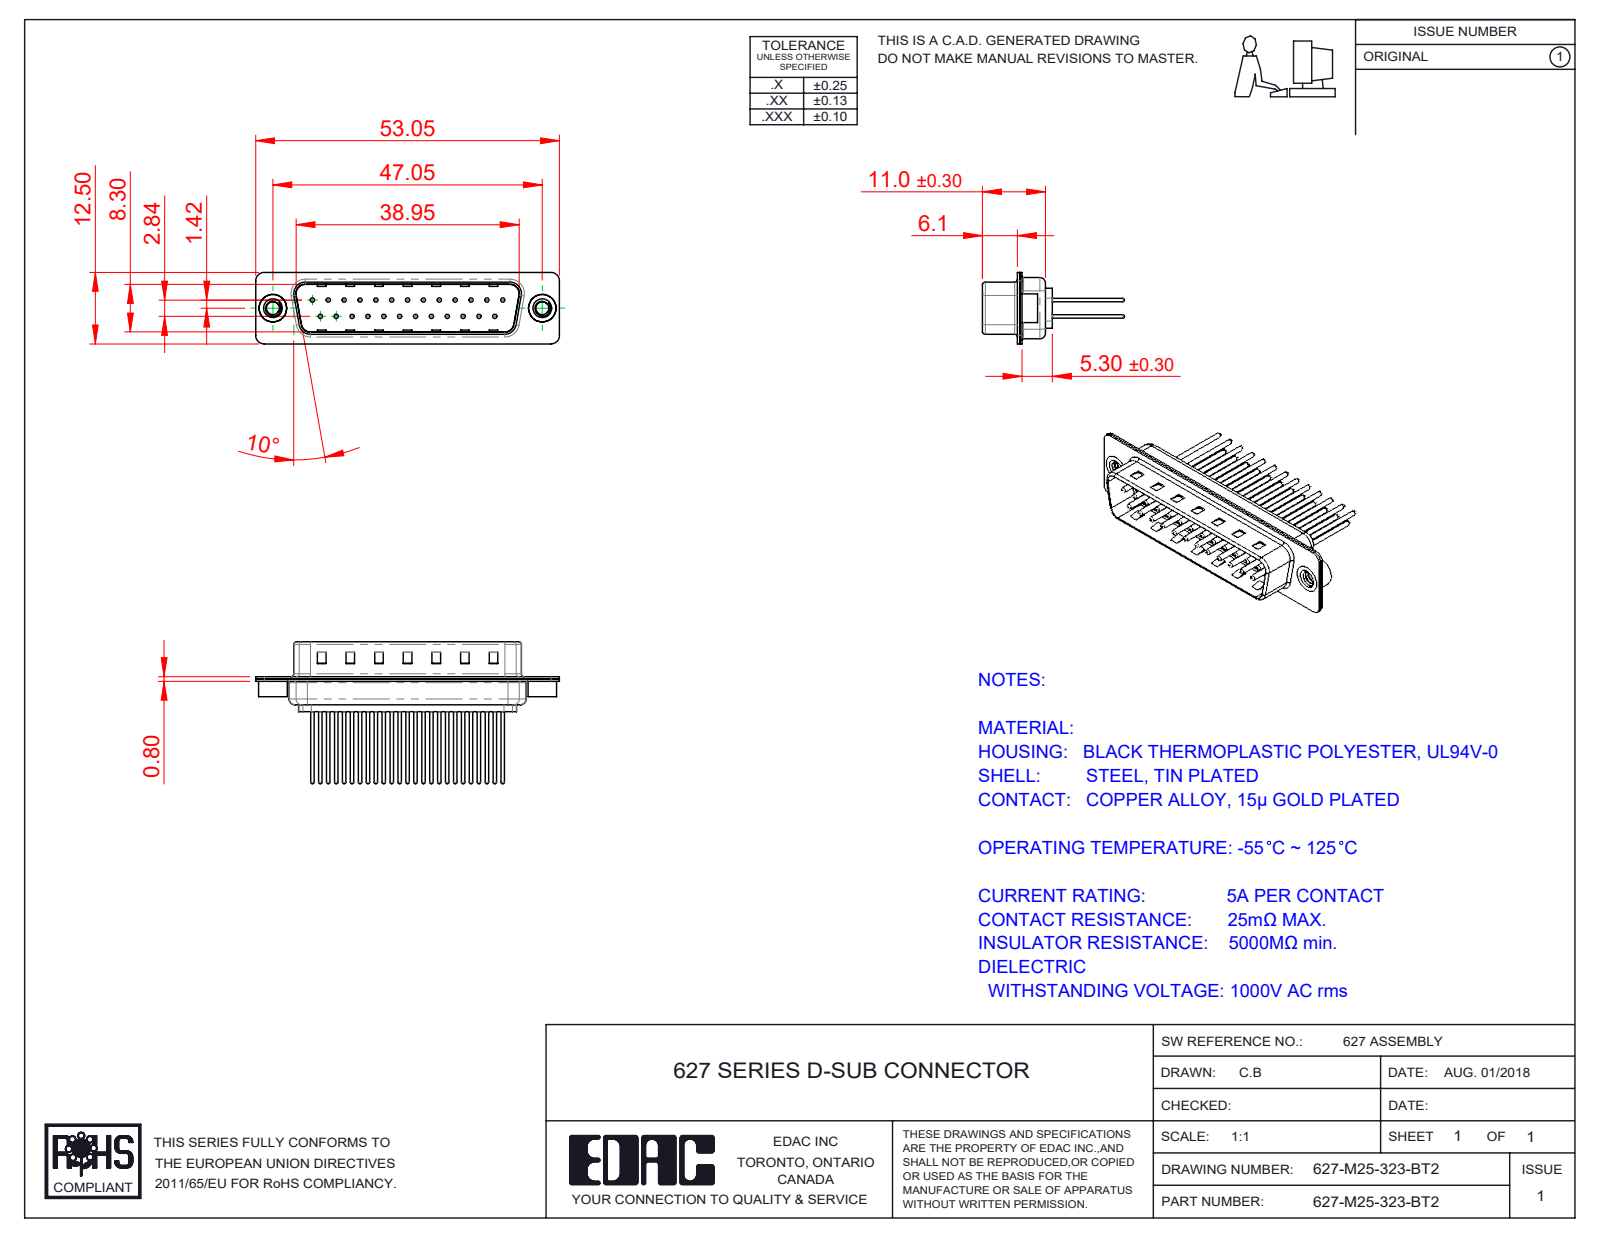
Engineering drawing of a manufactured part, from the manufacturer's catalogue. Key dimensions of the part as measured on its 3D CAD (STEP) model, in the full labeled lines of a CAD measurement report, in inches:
Part name (STEP PRODUCT): 627-M25-323-BT2; 627M Housing_25 Contacts; 627M Contact Row 2_23; 627M Shell Rear_25 Contacts (+3 more)
STEP written by: SolidWorks 2020 (CONFIG_CONTROL_DESIGN)
Units: inches
Bodies: 30 solids, 1301 faces (346 planar, 487 cylindrical, 468 other)
Overall size (bounding box): 2.089 × 0.975 × 0.492
Volume: 0.169 in³ · Surface area: 11.11 in²
Round holes (diameter × count): ⌀0.03 ×25, ⌀0.063 ×25, ⌀0.079 ×25, ⌀0.089 ×2, ⌀0.157 ×2, ⌀0.189 ×2
Round bosses / shafts (diameter × count): ⌀0.059 ×25, ⌀0.024 ×25, ⌀0.197 ×2, ⌀0.193 ×2
Partial cylindrical surfaces — rounded edges, fillets, slot ends (radius × count): R0.059 ×16, R0.079 ×12, R0.02 ×8, R0.063 ×8, R0.01 ×4, R0.024 ×4, R0.026 ×4, R0.035 ×4
Main face-to-face distances: 0.016, 0.031, 0.374, 0.358, 0.343, 0.39, 0.047, 0.24, 0.224, 0.03
Hole centre spacings: 0.124, 0.109, 0.218, 0.327, 0.436, 0.545, 0.654, 0.198
